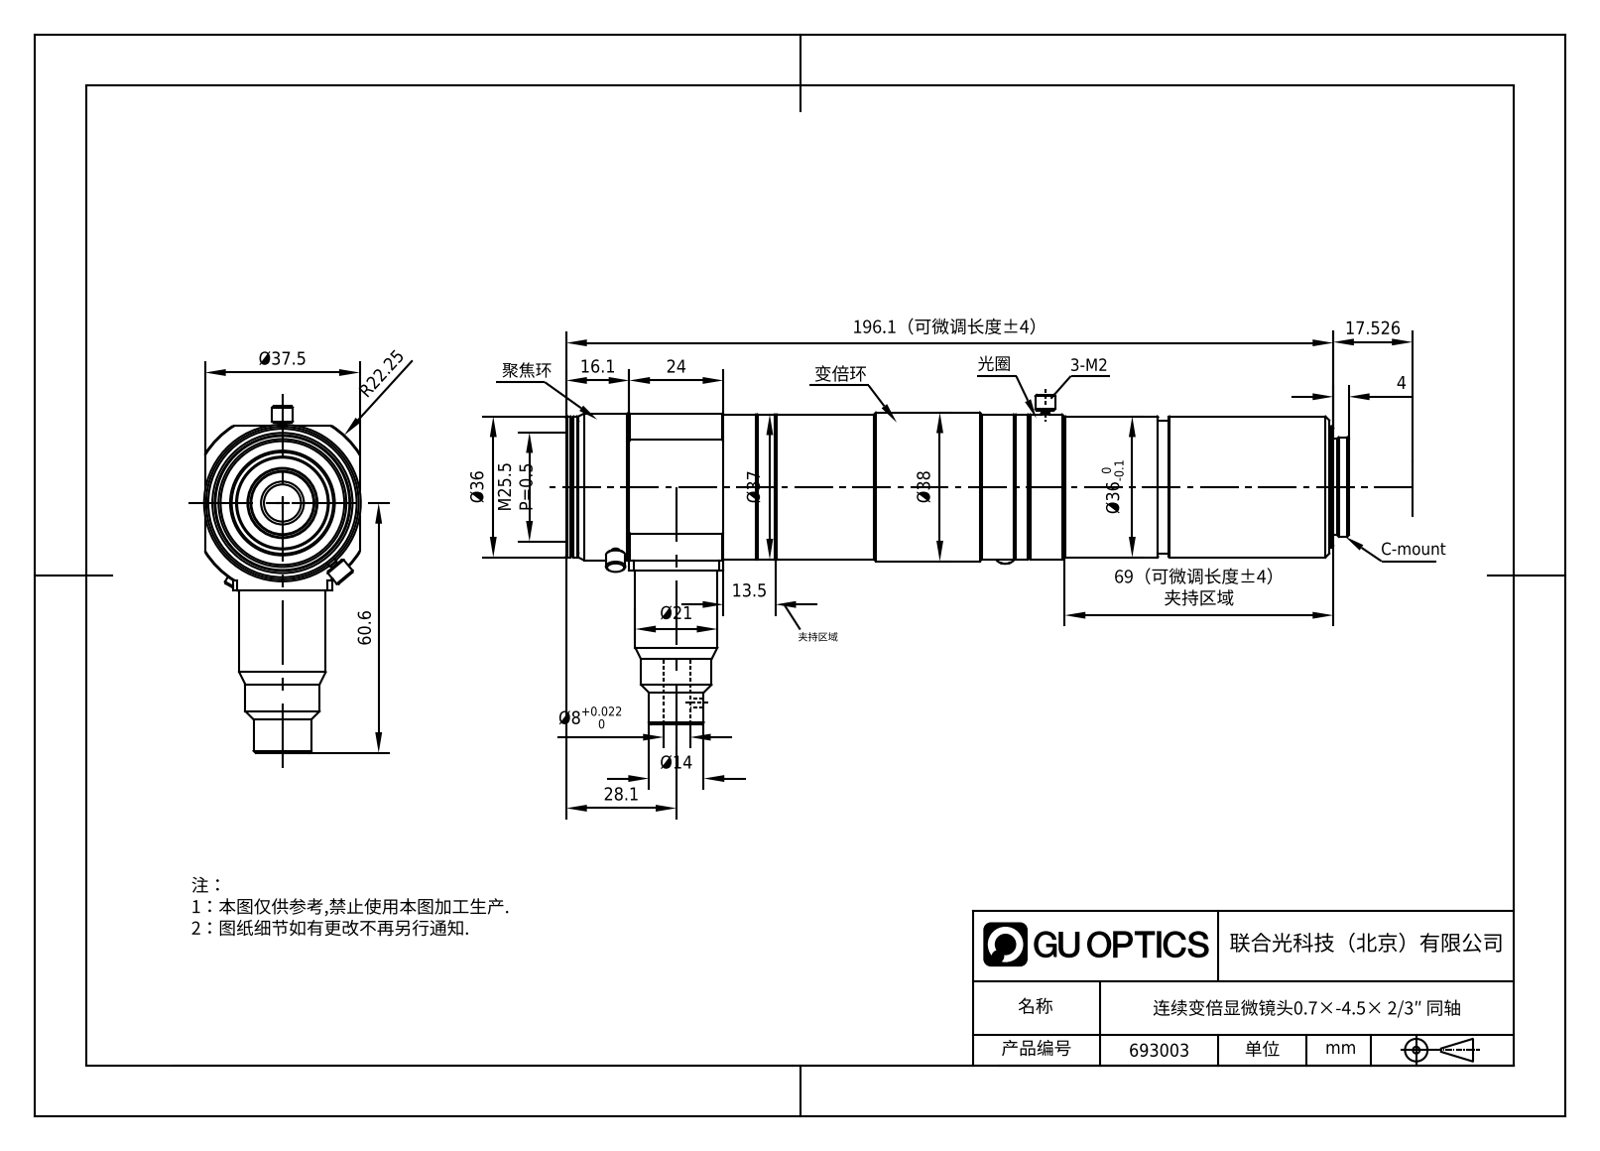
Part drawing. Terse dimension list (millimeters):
name: VSZ-0745CO
written by: SolidWorks 2012 (CONFIG_CONTROL_DESIGN)
unit: mm
bodies: 1 solid, 281 faces (51 planar, 96 cylindrical, 134 other)
size: 199.85 × 84.1 × 38
volume: 191 744 mm³; area: 38 802 mm²
holes: 1× ⌀8, 1× ⌀9, 1× ⌀9.01, 1× ⌀20, 1× ⌀22, 1× ⌀24, 1× ⌀24.5, 1× ⌀25, 1× ⌀25.5, 1× ⌀27.5, 1× ⌀28, 1× ⌀32.5
bosses: 3× ⌀5, 3× ⌀2, 3× ⌀1.6, 1× ⌀38, 1× ⌀37.5, 1× ⌀37, 1× ⌀36, 1× ⌀33.9
rounds: 1× R16.25, 1× R22.25
face distances: 37.5, 24, 115, 13, 13.9, 37.9, 115.2, 193.64, 179.74, 155.74
